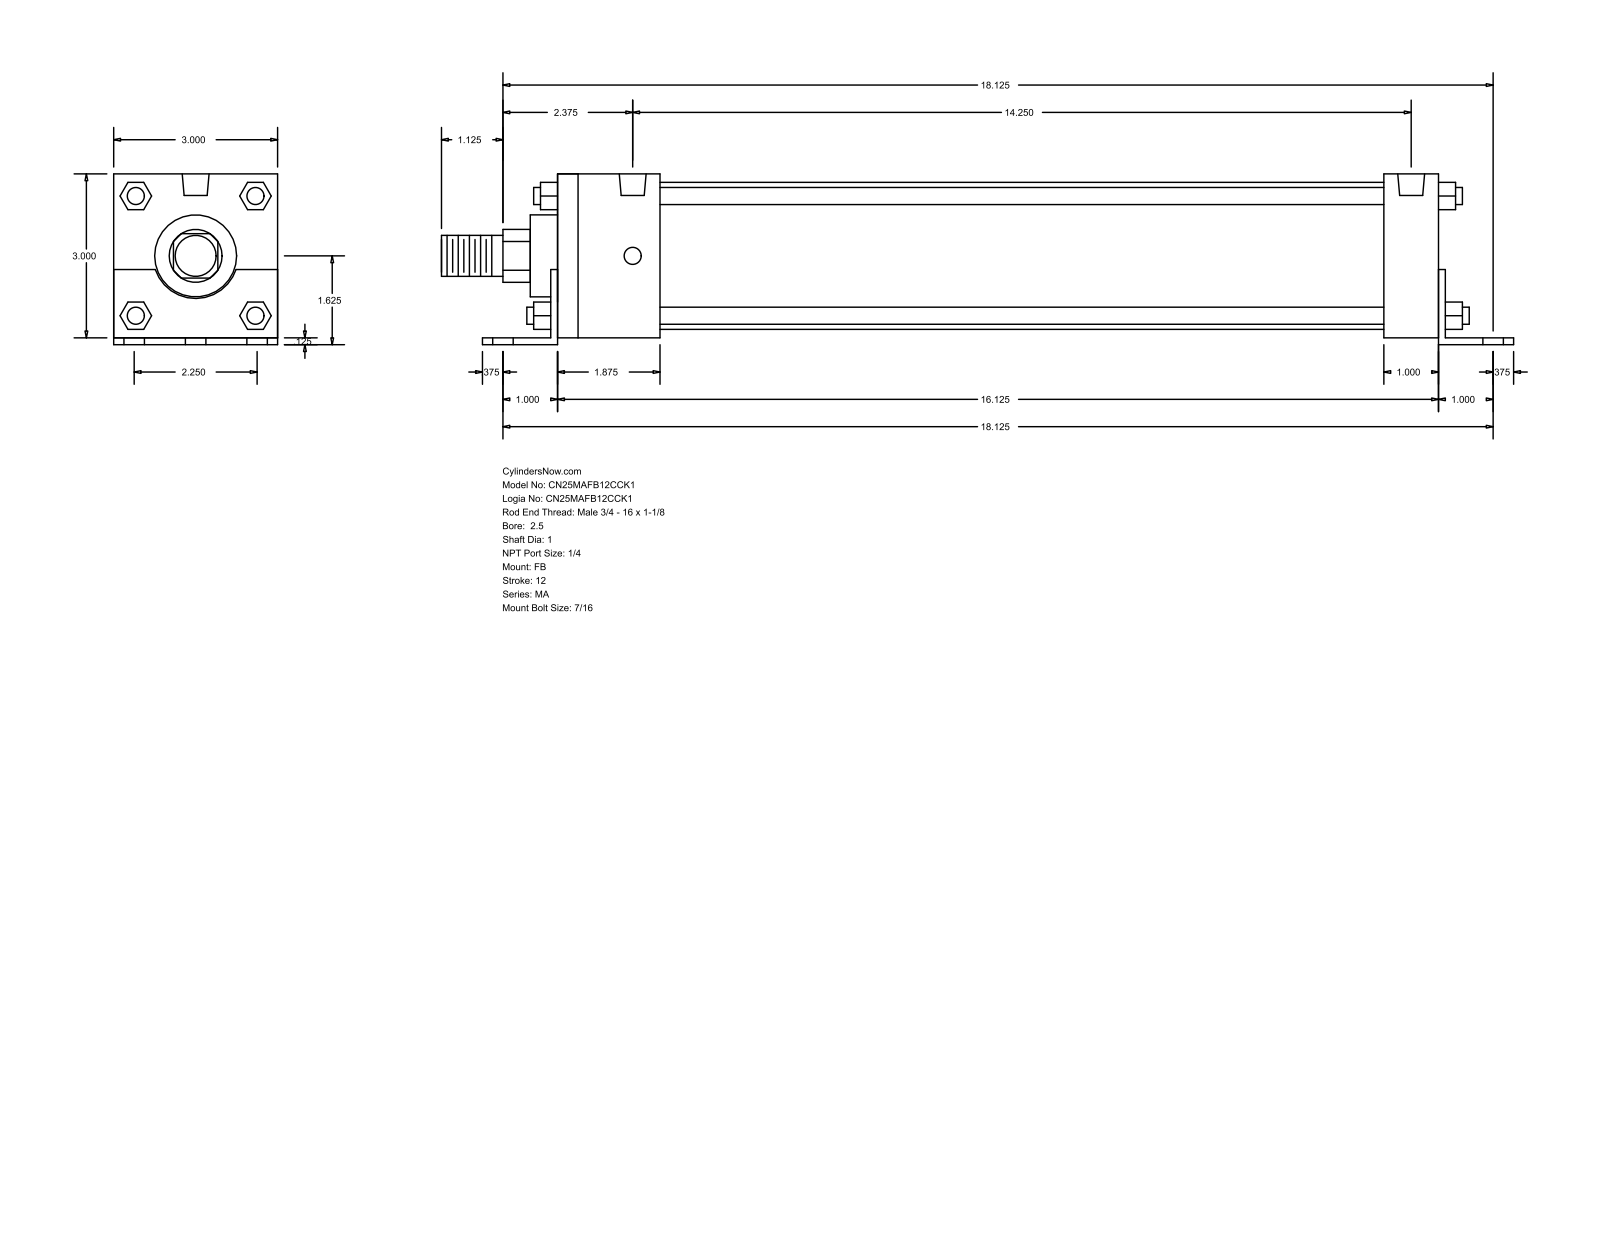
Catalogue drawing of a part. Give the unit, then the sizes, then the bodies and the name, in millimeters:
Units: millimetres
Overall size (bounding box): 498.48 × 79.38 × 76.2
Round holes (diameter × count): ⌀11.11 ×6, ⌀7.94 ×4, ⌀12.49 ×2
Round bosses / shafts (diameter × count): ⌀7.94 ×4, ⌀68.33 ×1, ⌀38.1 ×1, ⌀25.4 ×1, ⌀19.05 ×1
Partial cylindrical surfaces — rounded edges, fillets, slot ends (radius × count): R12.29 ×1, R19.81 ×1
Main face-to-face distances: 76.2, 3.17, 79.37, 412.75, 409.58, 12.7, 50.8, 47.63, 361.95, 365.12
Hole centre spacings: 28.57, 461.27, 460.38, 47.63, 57.14, 66.75, 361.94, 401.07
Bodies: 0 solids, 140 faces (105 planar, 35 cylindrical, 0 other)
Part name (STEP PRODUCT): MA_FB__0250_1
STEP written by: GSSL Pune (CONFIG_CONTROL_DESIGN)
